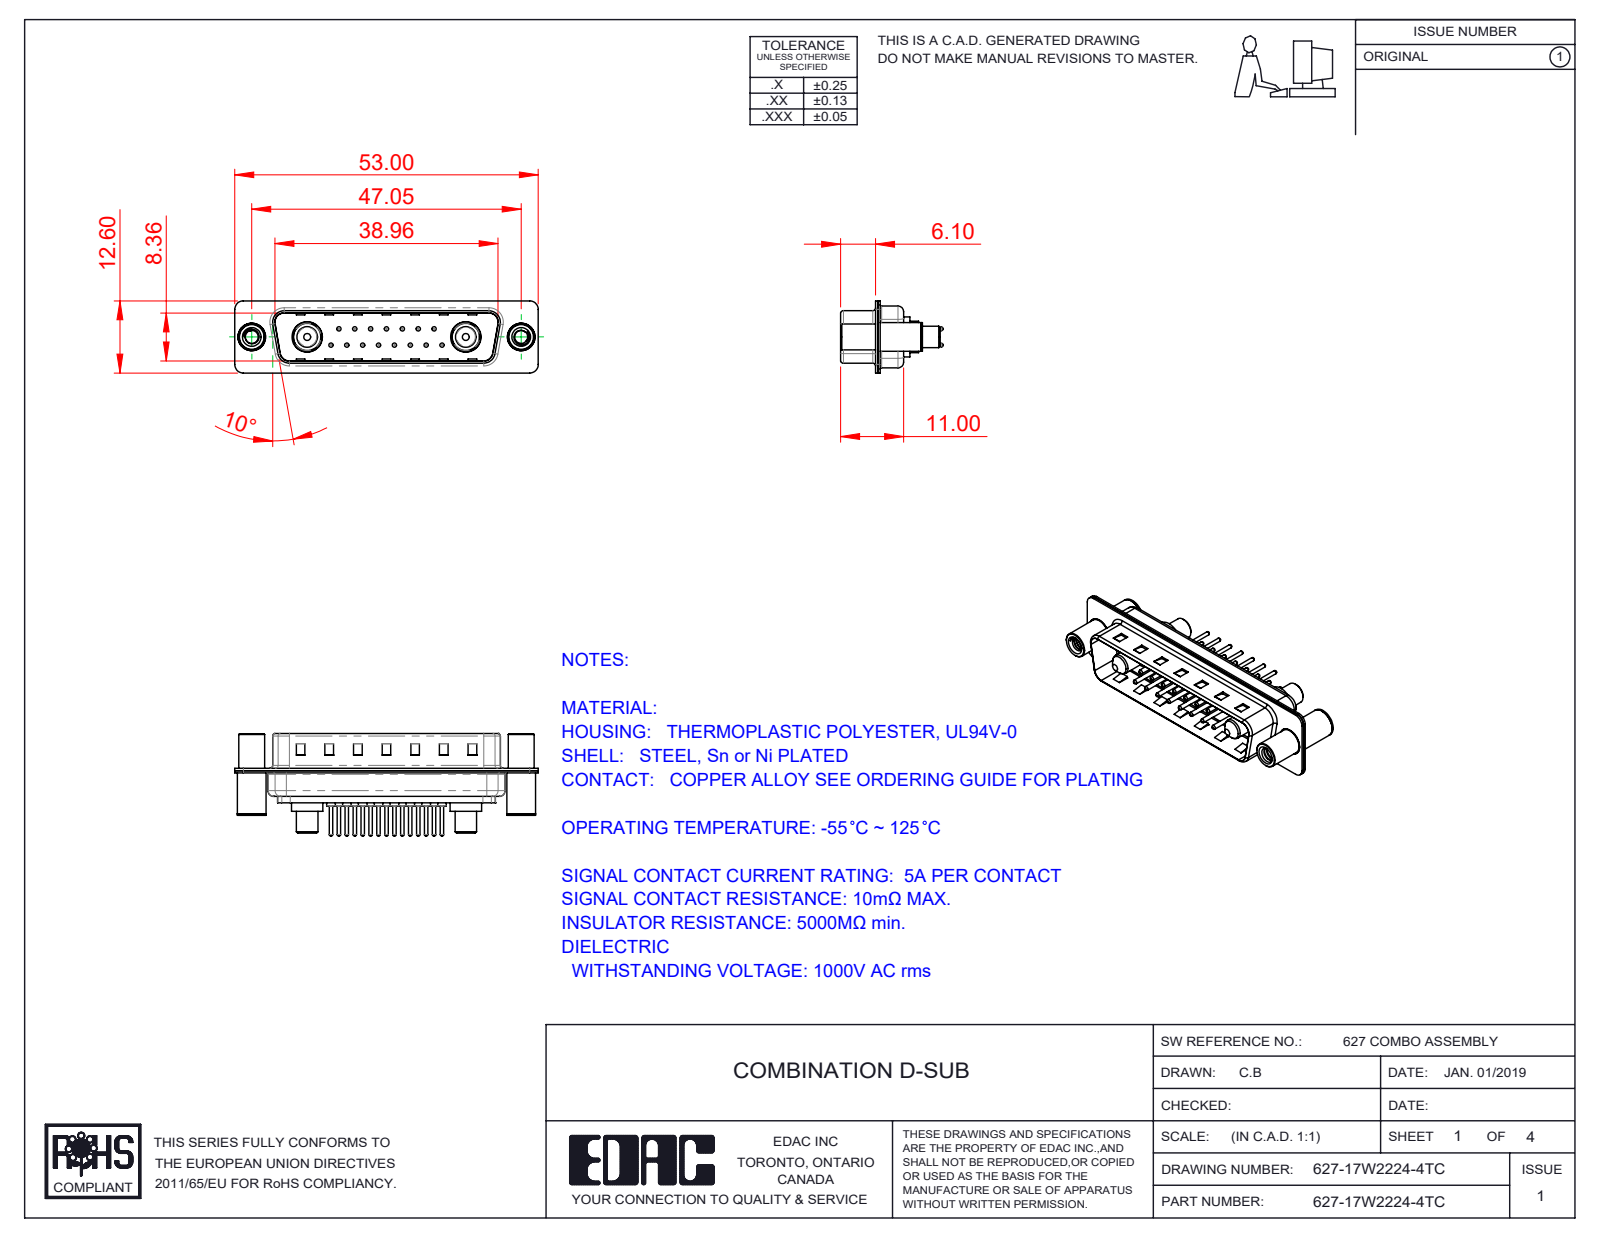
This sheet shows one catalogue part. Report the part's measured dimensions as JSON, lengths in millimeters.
{"part_name": "627Combo Shell Rear_25 Contacts; 627Combo Housing_17W2; 627Combo Contact Row 1_24; 627-17W2224-4TC (+5 more)", "step_written_by": "SolidWorks 2016 (CONFIG_CONTROL_DESIGN)", "units": "millimeters", "bodies": {"solids": 24, "faces": 1106, "planar": 302, "cylindrical": 447, "other": 357}, "overall_size": [53, 17.9, 12.6], "volume_mm3": 3183, "surface_area_mm2": 7338, "round_holes": [[0.75, 15], [1.6, 15], [2, 15], [2.26, 2], [3.26, 2], [4, 2], [4.8, 2], [4.85, 2], [5.3, 2]], "round_bosses_or_shafts": [[1.5, 15], [0.6, 15], [5.5, 2], [5.2, 2], [5, 2], [4.9, 2], [4.75, 2], [4.5, 2]], "partial_cylinders_radius": [[1.5, 16], [2, 12], [0.5, 8], [1.6, 8], [0.25, 4], [0.6, 4], [0.65, 4], [0.9, 4]], "face_to_face_distances": [0.4, 0.82, 9.58, 8.76, 1.5, 5.6, 6, 5.2, 0.8, 1.22], "hole_center_spacings": [3.16, 2.77, 5.54, 8.31, 5.04, 7.49, 11.08, 5.03]}
